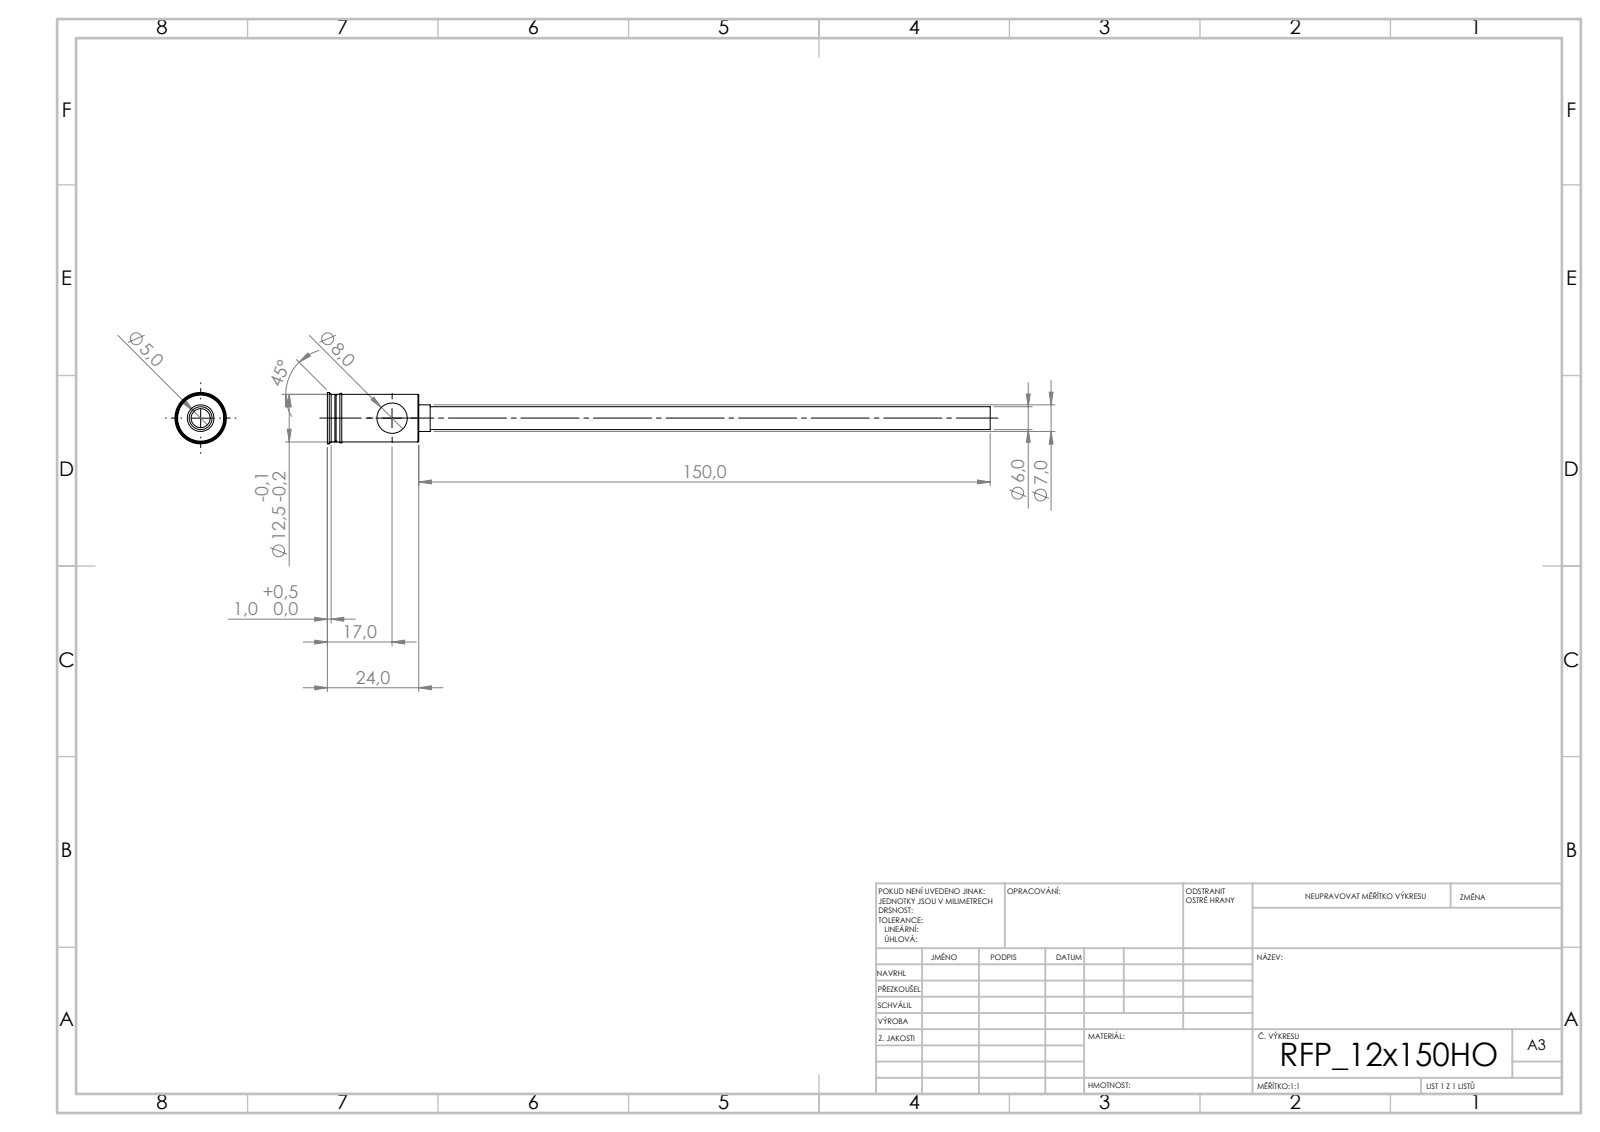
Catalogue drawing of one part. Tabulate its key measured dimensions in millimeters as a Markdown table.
| quantity | value |
| --- | --- |
| STEP written by | SolidWorks 2019 (CONFIG_CONTROL_DESIGN) |
| units | millimeters |
| bodies | 1 solid, 44 faces (20 planar, 16 cylindrical, 8 other) |
| overall size | 174 × 13.5 × 13.5 |
| volume | 3 524 mm³ |
| surface area | 6 677 mm² |
| round holes (diameter × count) | 5 × 1, 8 × 1 |
| round bosses / shafts (diameter × count) | 13.5 × 1, 12.5 × 1, 7 × 1, 6 × 1 |
| main face-to-face distances | 24, 22, 2, 7.9, 21.7, 2.3, 3, 24.7, 25, 27 |
